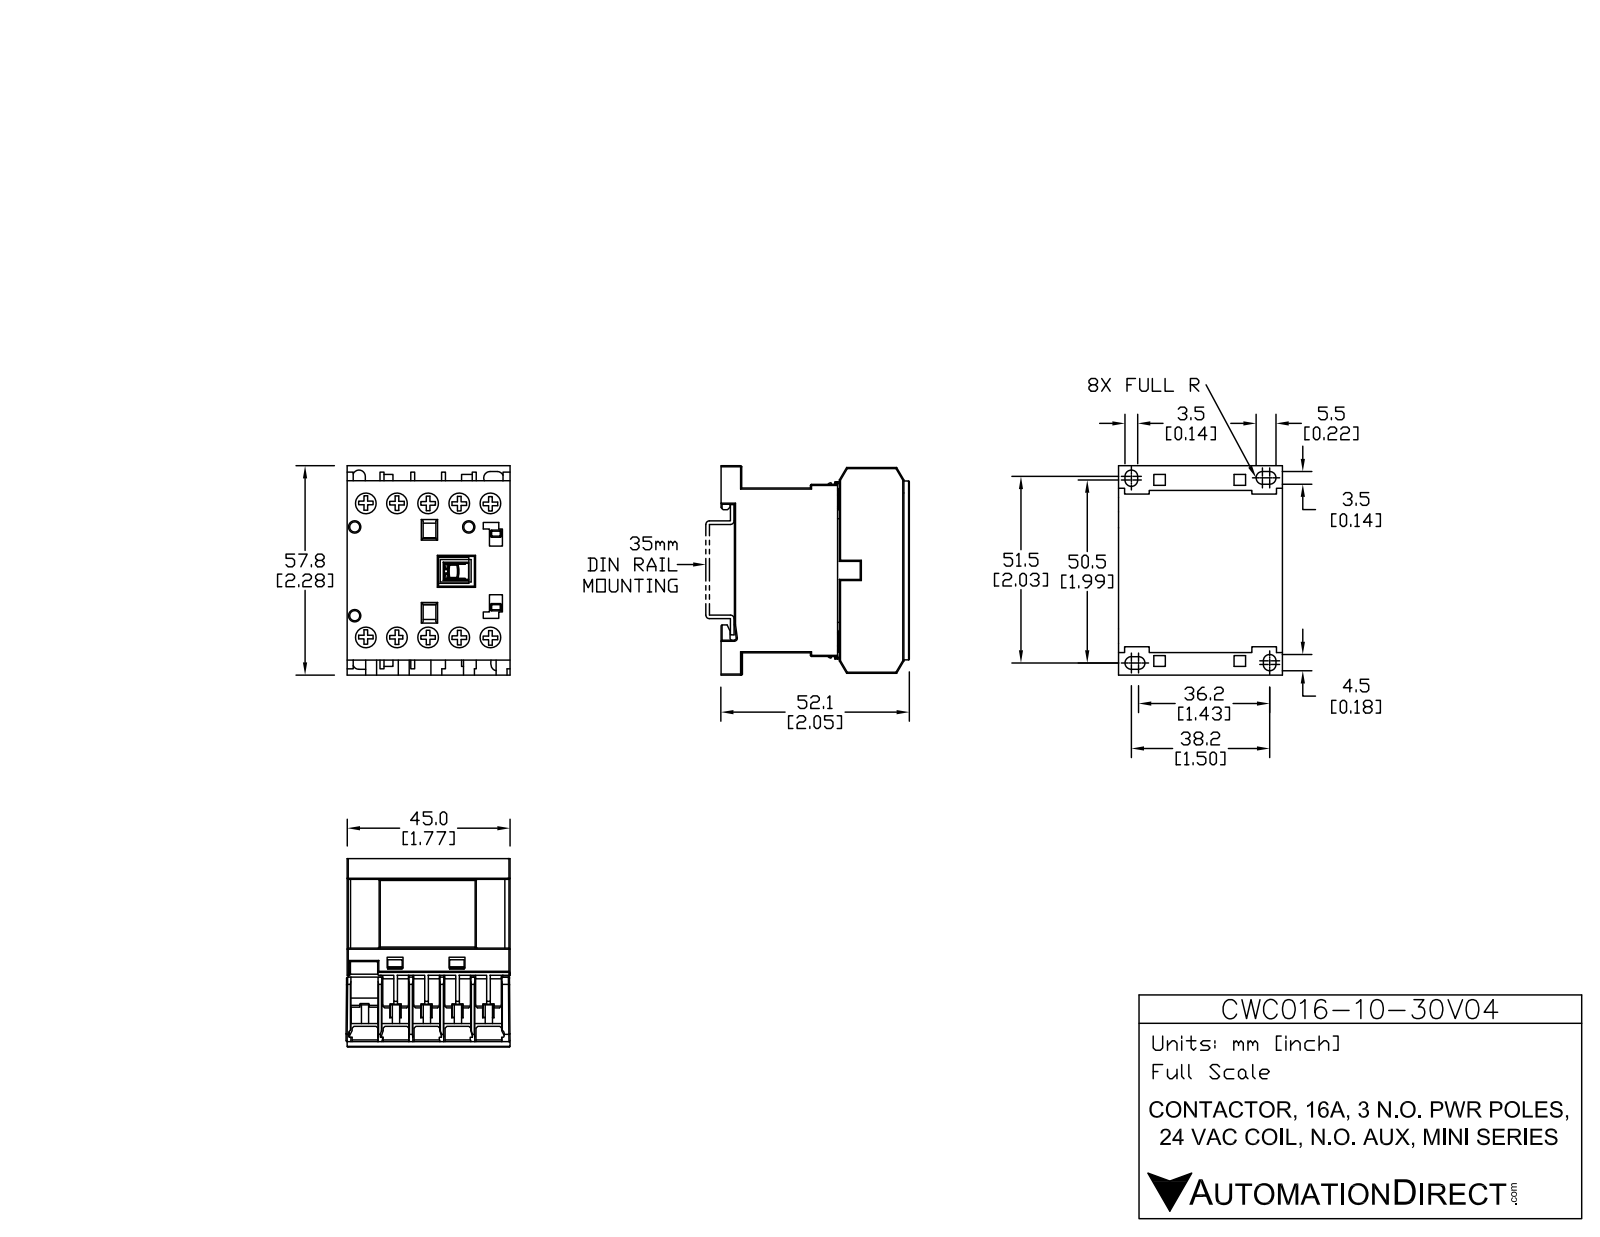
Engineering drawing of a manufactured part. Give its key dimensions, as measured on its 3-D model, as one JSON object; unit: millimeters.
{"part_name": "CWC16-10-30V04", "step_written_by": "SolidWorks 2013 (AUTOMOTIVE_DESIGN)", "units": "millimeters", "bodies": {"solids": 15, "faces": 535, "planar": 445, "cylindrical": 90, "other": 0}, "overall_size": [58.04, 52.12, 45.75], "volume_mm3": 97133, "surface_area_mm2": 30437, "round_holes": [[6.2, 10], [2.8, 3]], "round_bosses_or_shafts": [[5.9, 10]], "partial_cylinders_radius": [[0.3, 20], [1.72, 6], [1.73, 2], [0.32, 1], [0.42, 1], [0.55, 1]], "face_to_face_distances": [8.25, 45.5, 1.25, 16.5, 9.5, 5.5, 17.75, 5.13, 10.63, 7], "hole_center_spacings": [8.55, 37.94, 17.1, 40.72, 36.96, 25.65, 44.99, 6.91]}
